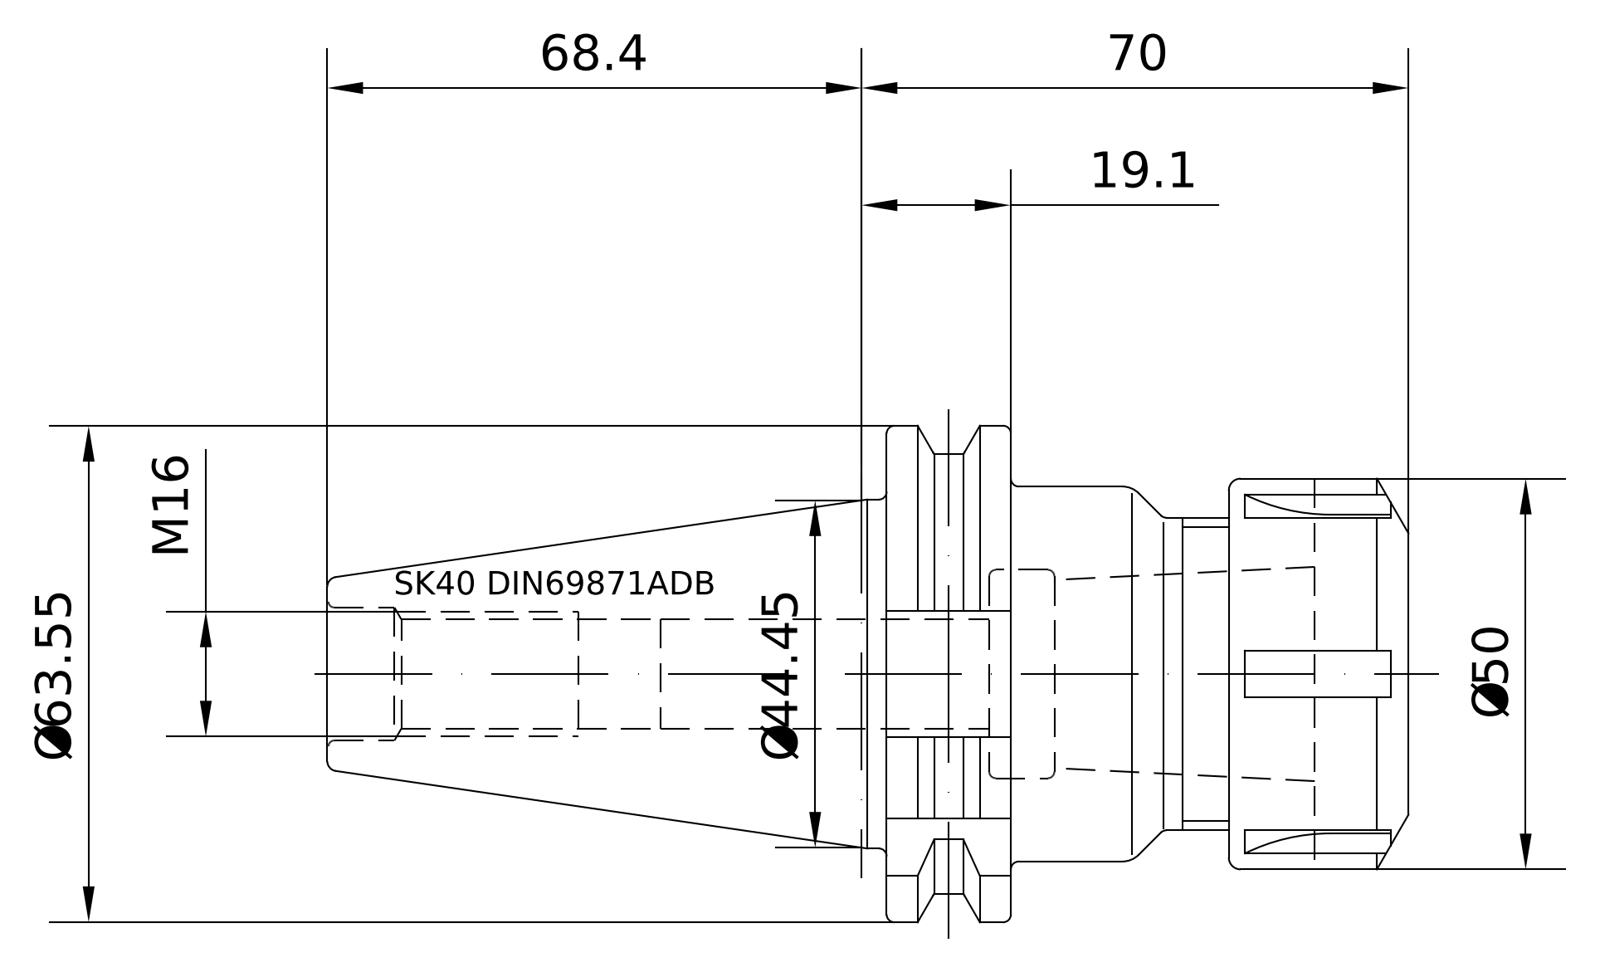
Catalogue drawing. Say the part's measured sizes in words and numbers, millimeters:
The part is named "40-320-32; 83-912-32; 40-320-32_ASM". Its 3-D file was written by "PRO/ENGINEER BY PARAMETRIC TECHNOLOGY CORPORATION, 2010430 (CONFIG_CONTROL_DESIGN)". It is 2 solids with 144 faces: 49 planar, 34 cylindrical and 61 other. Overall it measures 138.25 by 63.52 by 61.42 millimeters. Its volume is 176 236 cubic millimeters and its surface area 35 795 square millimeters. Round holes: 1 of diameter 13.84, 1 of diameter 17.01, 1 of diameter 17.5, 1 of diameter 23.5. Round bosses or shafts: 1 of diameter 50, 1 of diameter 48, 1 of diameter 43.75, 1 of diameter 40, 1 of diameter 16.01. Partial cylindrical surfaces (rounded edges, fillets, slot ends): 6 of radius 2.7, 1 of radius 1.35, 1 of radius 28, 1 of radius 31.76. The main face-to-face distances are 44.3, 66.8, 22.5, 15.85, 28.45, 50.95, 53.8, 37.95, 9.5, 13.
